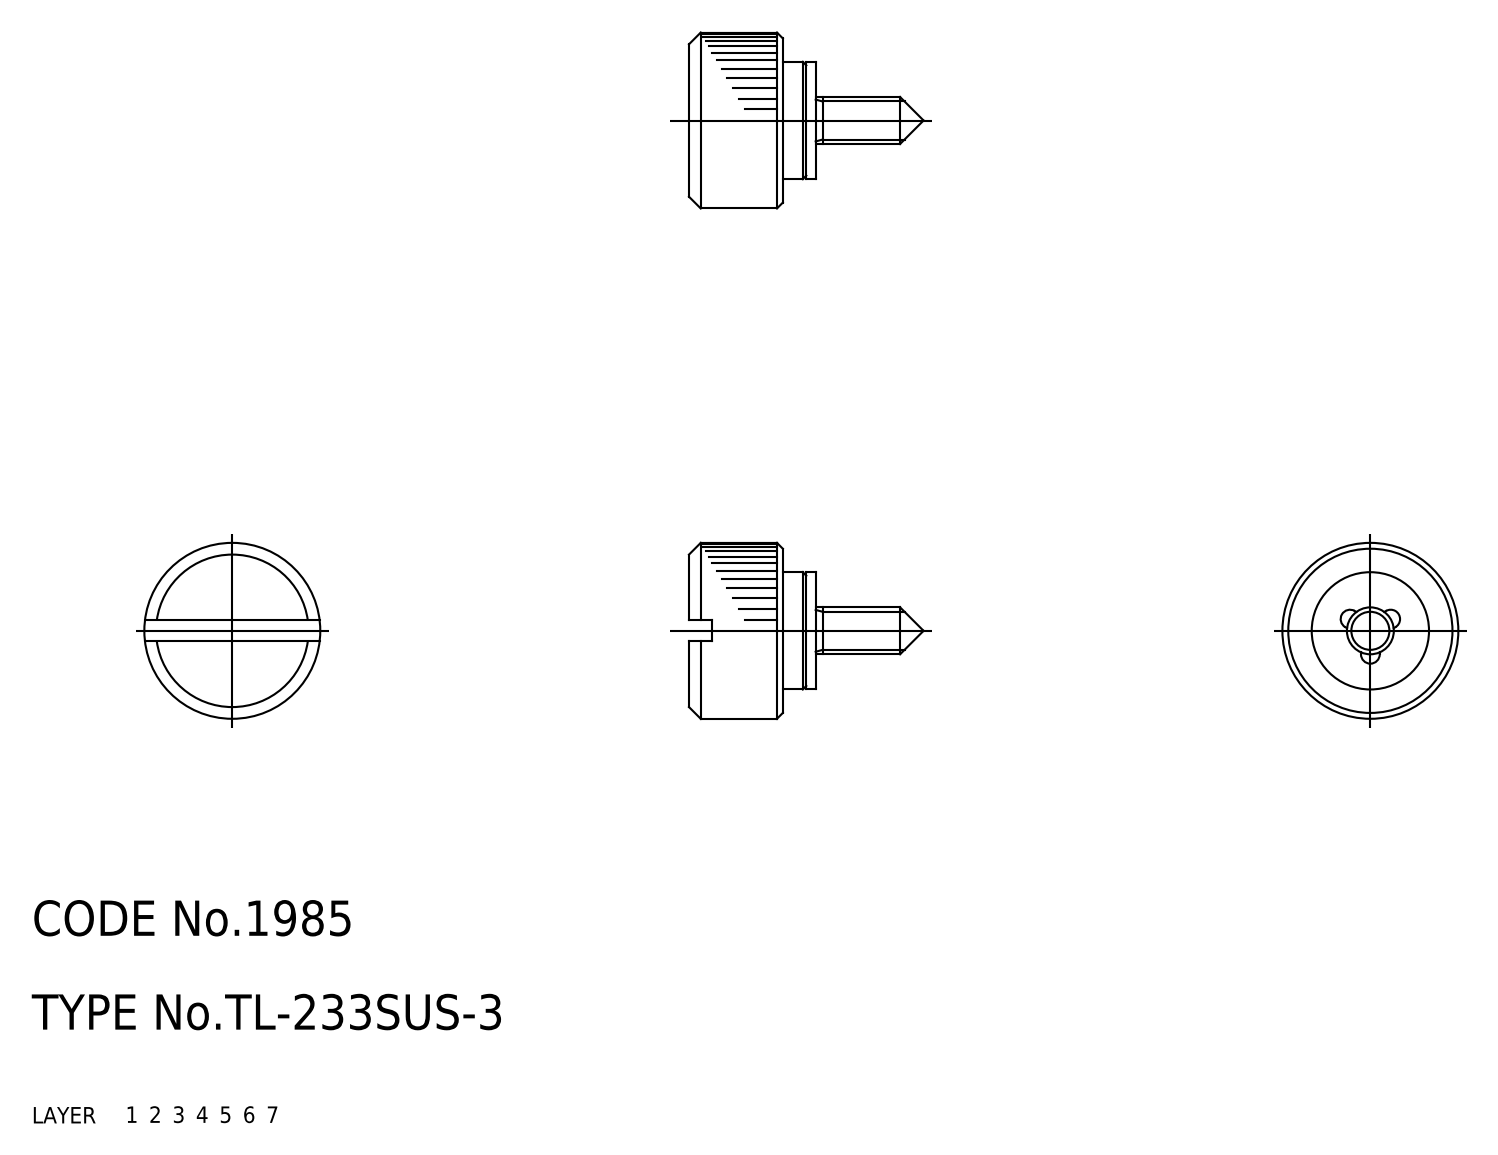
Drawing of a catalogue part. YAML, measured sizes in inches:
part_name: "washer; knob; TL_233SUS_3_29535_36"
step_written_by: "CADfix (AUTOMOTIVE_DESIGN)"
units: inches
bodies: {solids: 2, faces: 37, planar: 0, cylindrical: 0, other: 37}
overall_size: [0.787, 0.591, 0.591]
volume: 0.101
surface_area: 1.654
